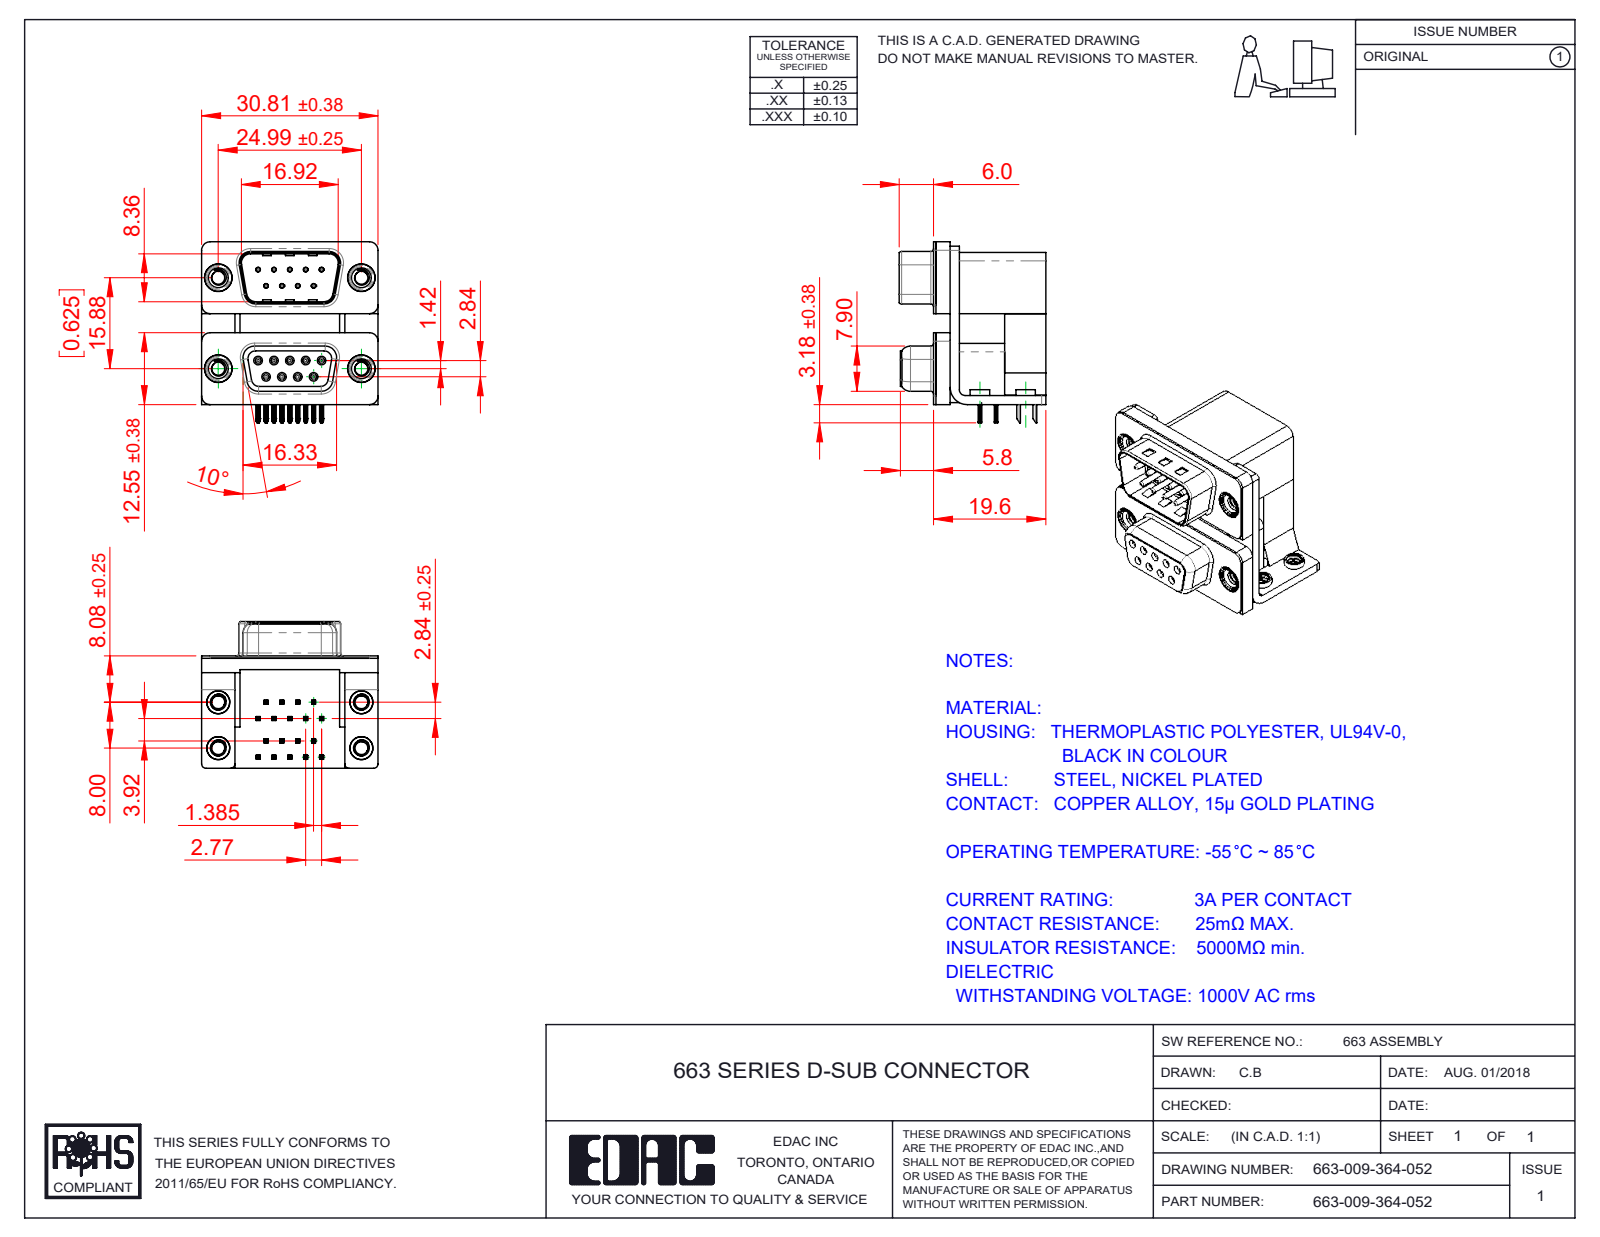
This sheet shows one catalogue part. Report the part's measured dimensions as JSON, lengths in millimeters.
{"part_name": "663 Housing Spacer_09 Contacts L; 663 Contact Top Upper_L; 663 4-40 Threaded Board Mount; 663 Shell Receptacle_09 Contacts (+8 more)", "step_written_by": "SolidWorks 2020 (CONFIG_CONTROL_DESIGN)", "units": "millimeters", "bodies": {"solids": 33, "faces": 2669, "planar": 1275, "cylindrical": 771, "other": 623}, "overall_size": [31.61, 30.81, 25.6], "volume_mm3": 10400, "surface_area_mm2": 12325, "round_holes": [[0.8, 18], [0.35, 9], [0.9, 9], [2.26, 8], [2.75, 4], [3.2, 4], [3.5, 4], [4, 4], [4.8, 4], [5, 4]], "round_bosses_or_shafts": [[1.2, 9], [0.75, 9], [4.9, 4], [4.75, 4], [4, 4], [3.9, 4], [3.4, 4]], "partial_cylinders_radius": [[0.1, 72], [0.15, 36], [0.25, 36], [0.12, 18], [0.35, 18], [1.5, 13], [0.5, 12], [0.34, 9]], "face_to_face_distances": [0.4, 2.5, 16.7, 19.2, 19.6, 2.9, 1.6, 7.2, 9.5, 12], "hole_center_spacings": [3.16, 2.77, 16.12, 15.88, 5.54, 16.82, 13.11, 18.77]}
